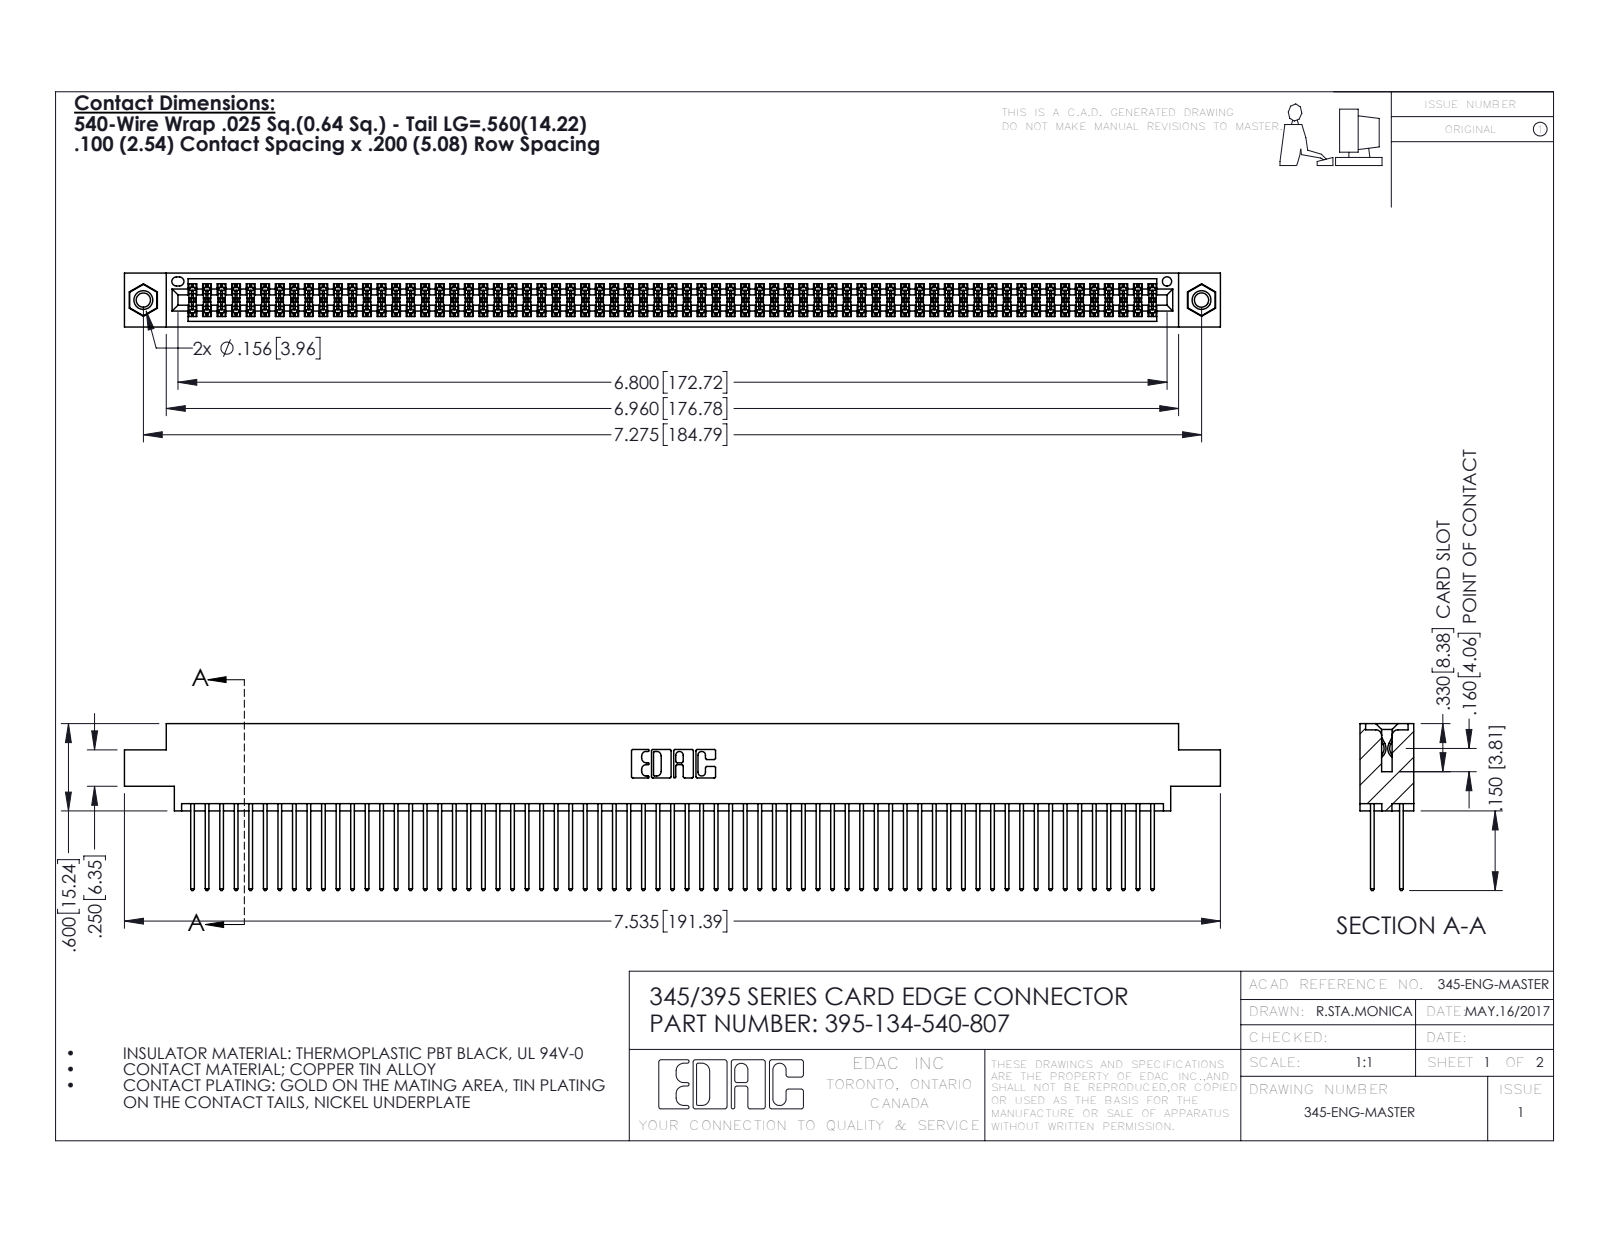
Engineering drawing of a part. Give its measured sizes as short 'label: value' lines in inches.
name: 345 Part_0.170 Offset - 0.156 Dia-TI; 395-134-540-807; 345-292-001_345-293-140; 345-250-001_345-250-005-103
written by: SolidWorks 2016 (CONFIG_CONTROL_DESIGN)
unit: in
bodies: 137 solids, 6890 faces (4538 planar, 2336 cylindrical, 16 other)
size: 7.535 × 1.147 × 0.37
volume: 1.172 in³; area: 48.67 in²
holes: 2× ⌀0.098, 2× ⌀0.125, 2× ⌀0.156, 1× ⌀0.064
bosses: 2× ⌀0.155
rounds: 201× R0.006, 134× R0.01, 22× R0.01, 6× R0.007, 6× R0.031, 3× R0.026, 2× R0.014, 2× R0.019
face distances: 0.072, 0.298, 0.2, 0.098, 0.272, 0.025, 0.37, 0.225, 0.175, 0.149
hole spacings: 0.27, 7.039, 7.275
